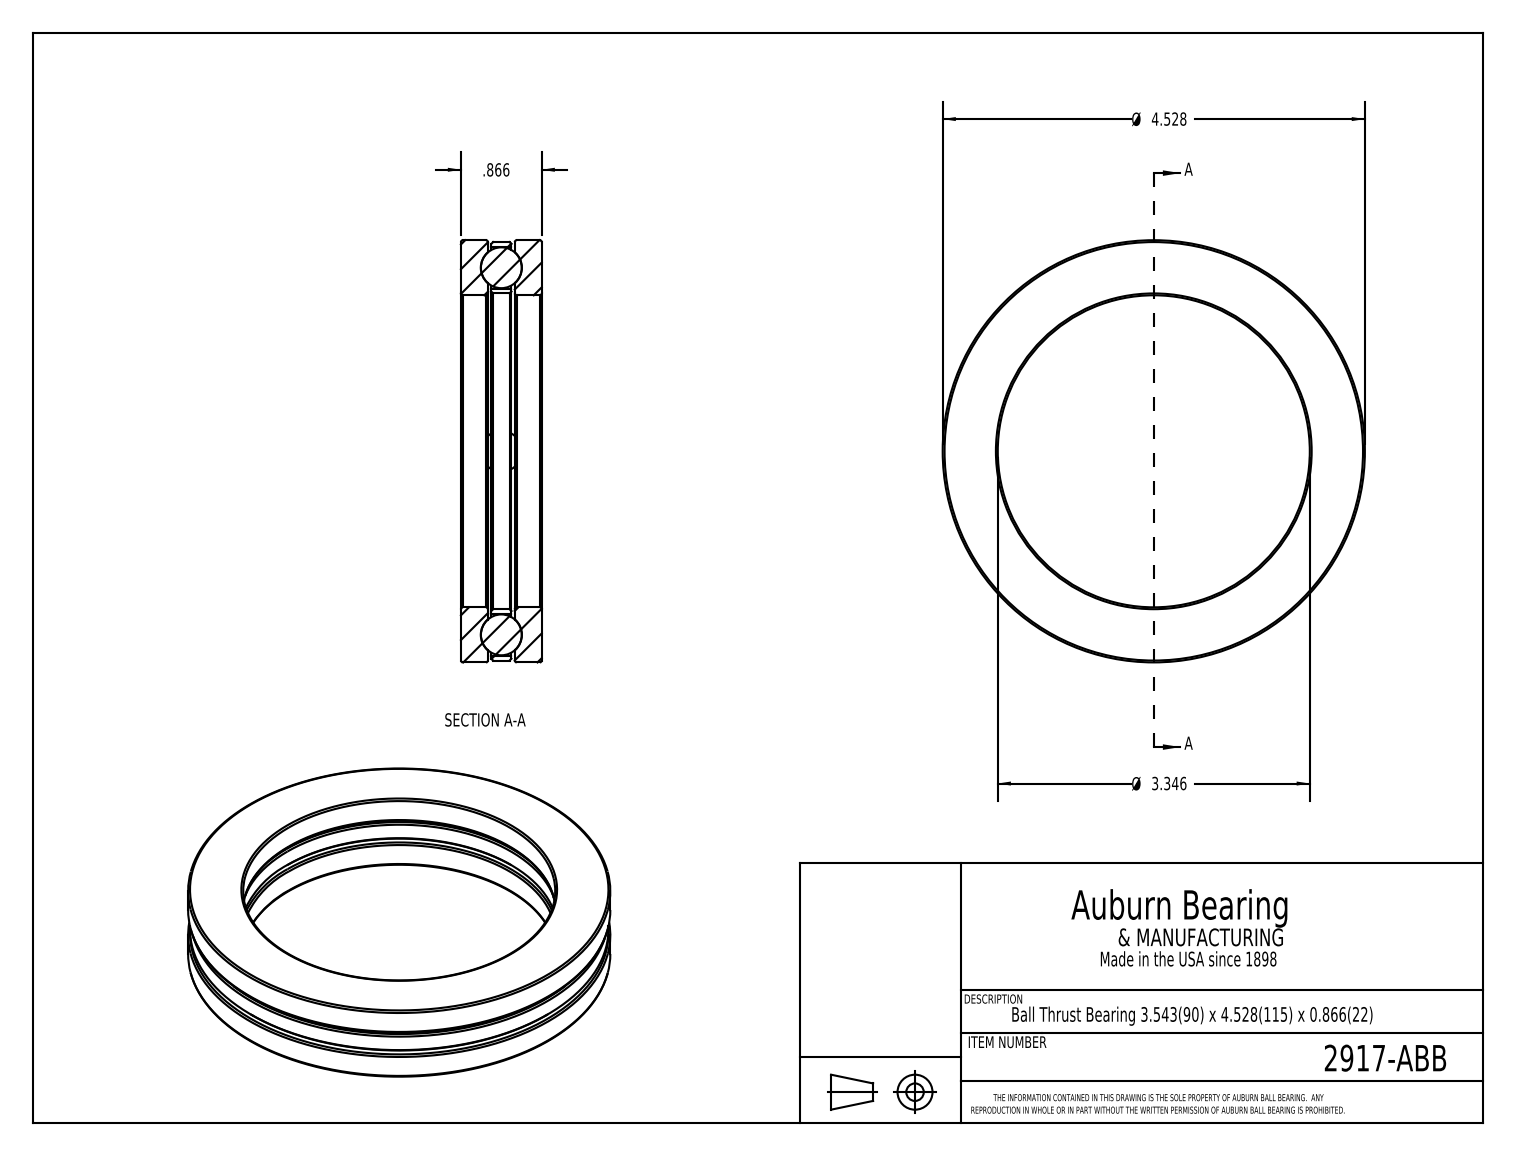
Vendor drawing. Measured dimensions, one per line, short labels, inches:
name: 2917-ABB
written by: SolidWorks 2017 (CONFIG_CONTROL_DESIGN)
unit: in
bodies: 7 solids, 42 faces (14 planar, 10 cylindrical, 18 other)
size: 4.528 × 4.528 × 0.866
volume: 4.435 in³; area: 58.53 in²
holes: 4× ⌀0.448, 1× ⌀3.543, 1× ⌀3.583
bosses: 1× ⌀4.528, 1× ⌀4.488
face distances: 0.325, 0.541, 0.866, 0.217, 0.289, 0.578, 0.036, 0.253, 0.289
hole spacings: 2.018, 2.854, 4.035
